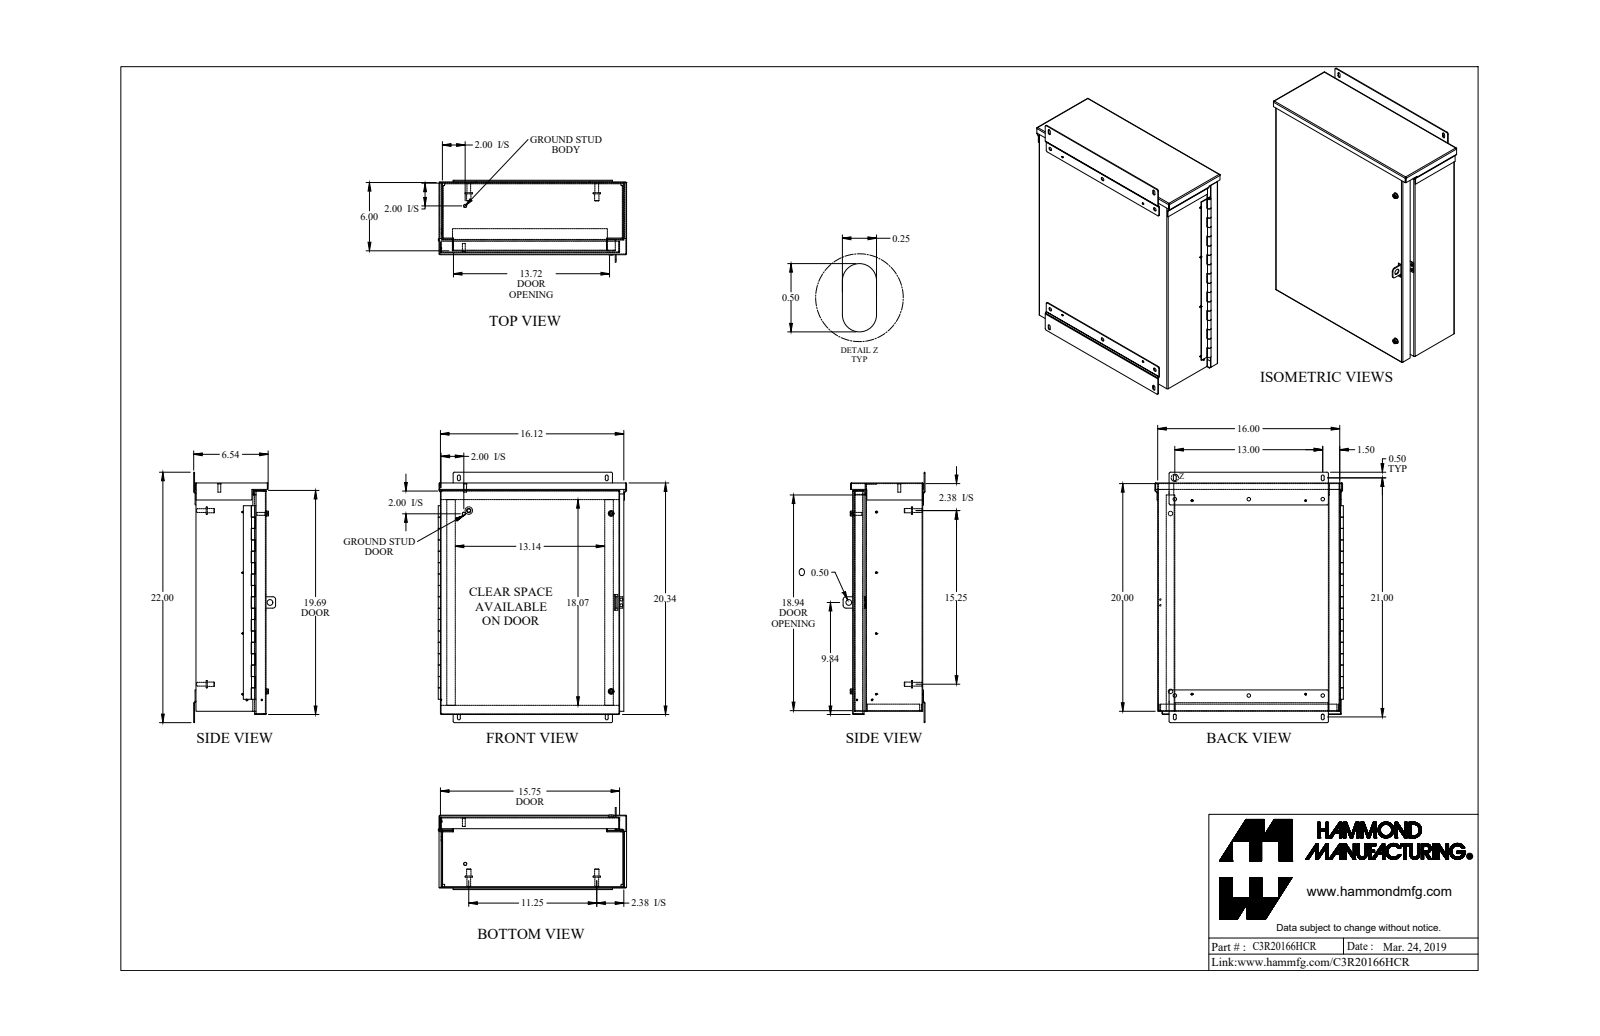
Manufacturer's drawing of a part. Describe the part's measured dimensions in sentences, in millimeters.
The part is named "C3R20166HCR_Default". Its 3-D file was written by "SolidWorks 2019 (CONFIG_CONTROL_DESIGN)". It is 33 solids with 860 faces: 487 planar, 319 cylindrical and 54 other. Overall it measures 558.8 by 420.5 by 182.8 millimeters. Its volume is 1 507 000 cubic millimeters and its surface area 1 925 000 square millimeters. Round holes: 9 of diameter 8, 4 of diameter 3.6, 3 of diameter 6.6, 2 of diameter 3.5, 2 of diameter 6.8, 2 of diameter 7.1, 2 of diameter 7.4, 2 of diameter 10.1, 1 of diameter 4.8, 1 of diameter 12.7. Round bosses or shafts: 10 of diameter 3.3, 4 of diameter 16.5, 4 of diameter 9.5, 4 of diameter 8.4, 3 of diameter 13, 3 of diameter 6.2, 3 of diameter 4.7, 2 of diameter 12.7. Partial cylindrical surfaces (rounded edges, fillets, slot ends): 26 of radius 0.7, 26 of radius 2.2, 19 of radius 3.2, 5 of radius 0.9, 5 of radius 2.7, 3 of radius 4.3, 2 of radius 6.4. The main face-to-face distances are 1.4, 154.9, 153.5, 156.4, 405, 508, 125.6, 24, 506.6, 29.4. The hole center spacings are 38.2, 127.1, 165.1, 292.1, 453.1, 48.2, 175, 177.7.
